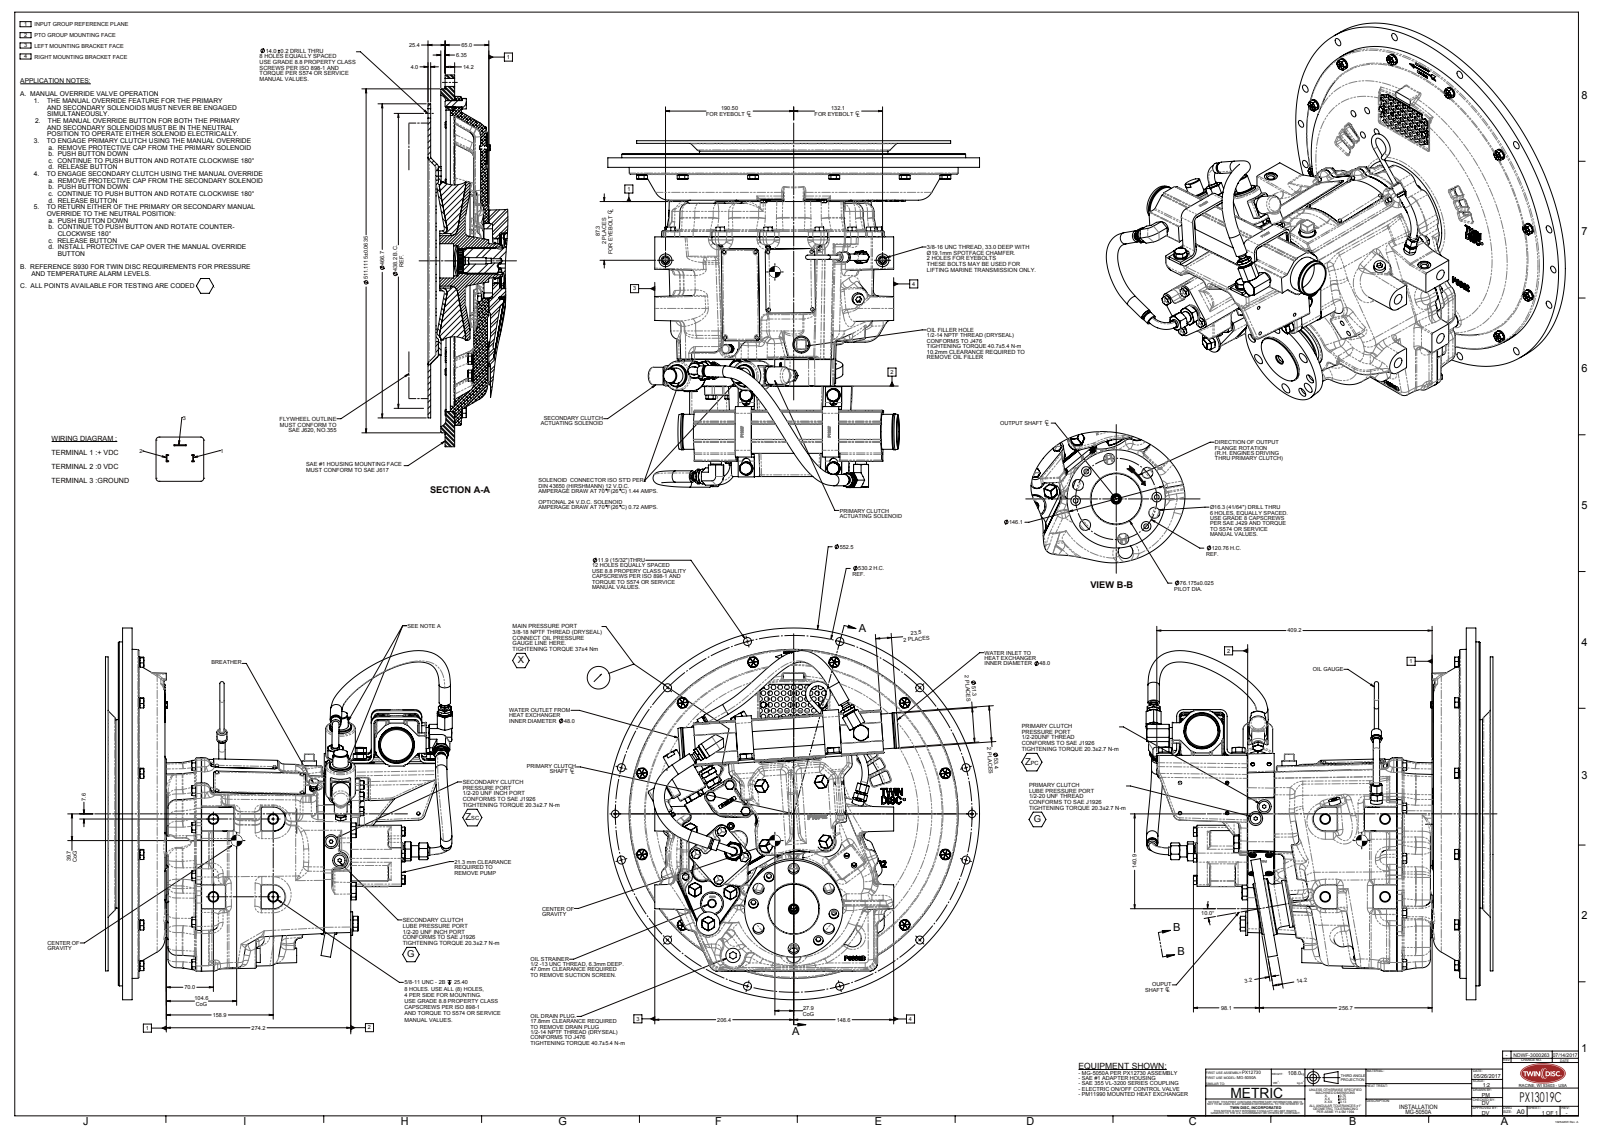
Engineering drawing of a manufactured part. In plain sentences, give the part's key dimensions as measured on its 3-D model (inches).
The part is named "PX13019C". Its 3-D file was written by "SolidWorks 2015 (AUTOMOTIVE_DESIGN)". It is 0 solids with 3669 faces: 1173 planar, 920 cylindrical and 1576 other. Overall it measures 21.75 by 21.75 by 20.293 inches. Round holes: 51 of diameter 0.276, 12 of diameter 0.323, 12 of diameter 0.469, 8 of diameter 0.313, 8 of diameter 0.551, 6 of diameter 0.641, 4 of diameter 0.197, 4 of diameter 0.281, 4 of diameter 0.406, 4 of diameter 0.563, 4 of diameter 0.813, 3 of diameter 0.406. Round bosses or shafts: 15 of diameter 0.63, 7 of diameter 0.557, 7 of diameter 0.372, 4 of diameter 0.781, 4 of diameter 0.748, 4 of diameter 0.665, 4 of diameter 0.394, 3 of diameter 0.743. Partial cylindrical surfaces (rounded edges, fillets, slot ends): 73 of radius 0.059, 68 of radius 0.32, 63 of radius 0.06, 51 of radius 0.315, 32 of radius 0.118, 31 of radius 0.016, 19 of radius 0.4, 18 of radius 0.098. The main face-to-face distances are 0.157, 1.402, 1.56, 1.921, 3.324, 3.481, 9.291, 11.213, 12.615, 12.772. The hole center spacings are 0.394, 0.395, 0.683, 0.787, 0.79, 1.042, 1.044, 1.181.
